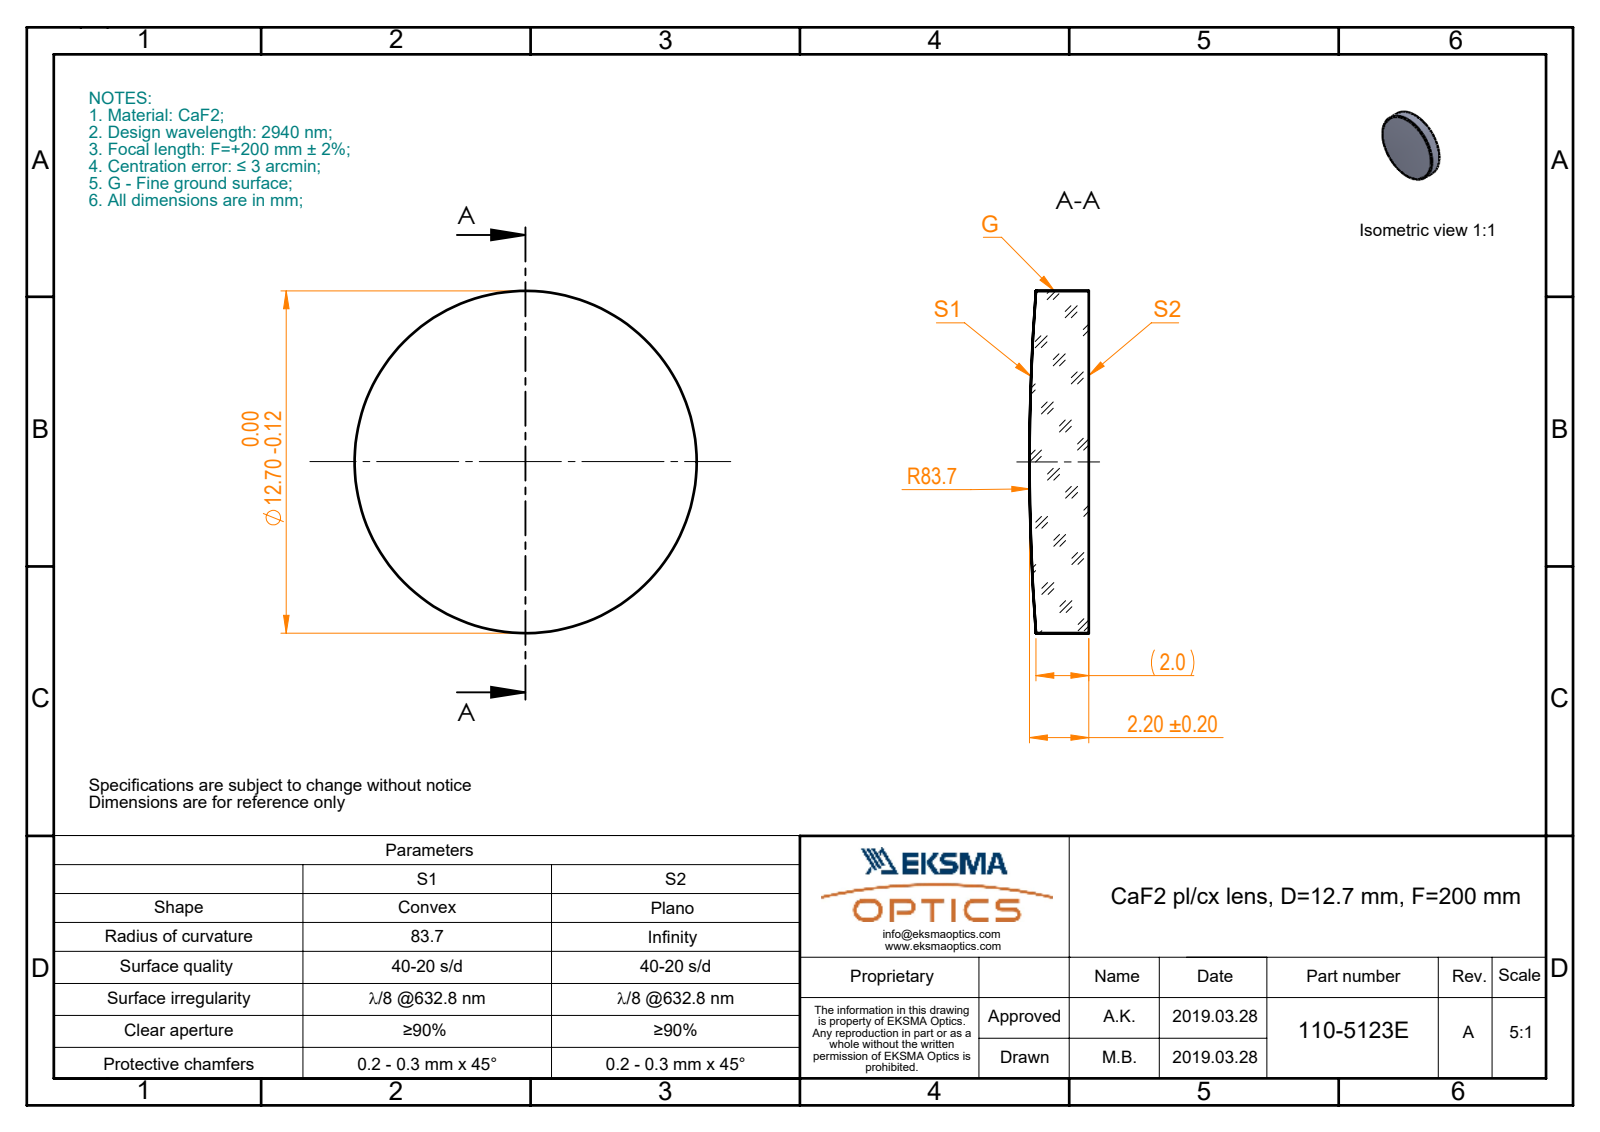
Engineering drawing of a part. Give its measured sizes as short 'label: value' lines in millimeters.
name: 110-5123E CaF2 pl-cx 12.7 F200
written by: SolidWorks 2017 (CONFIG_CONTROL_DESIGN)
unit: mm
bodies: 1 solid, 5 faces (1 planar, 2 cylindrical, 2 other)
size: 12.7 × 12.7 × 2.2
volume: 263 mm³; area: 332 mm²
bosses: 1× ⌀12.7
